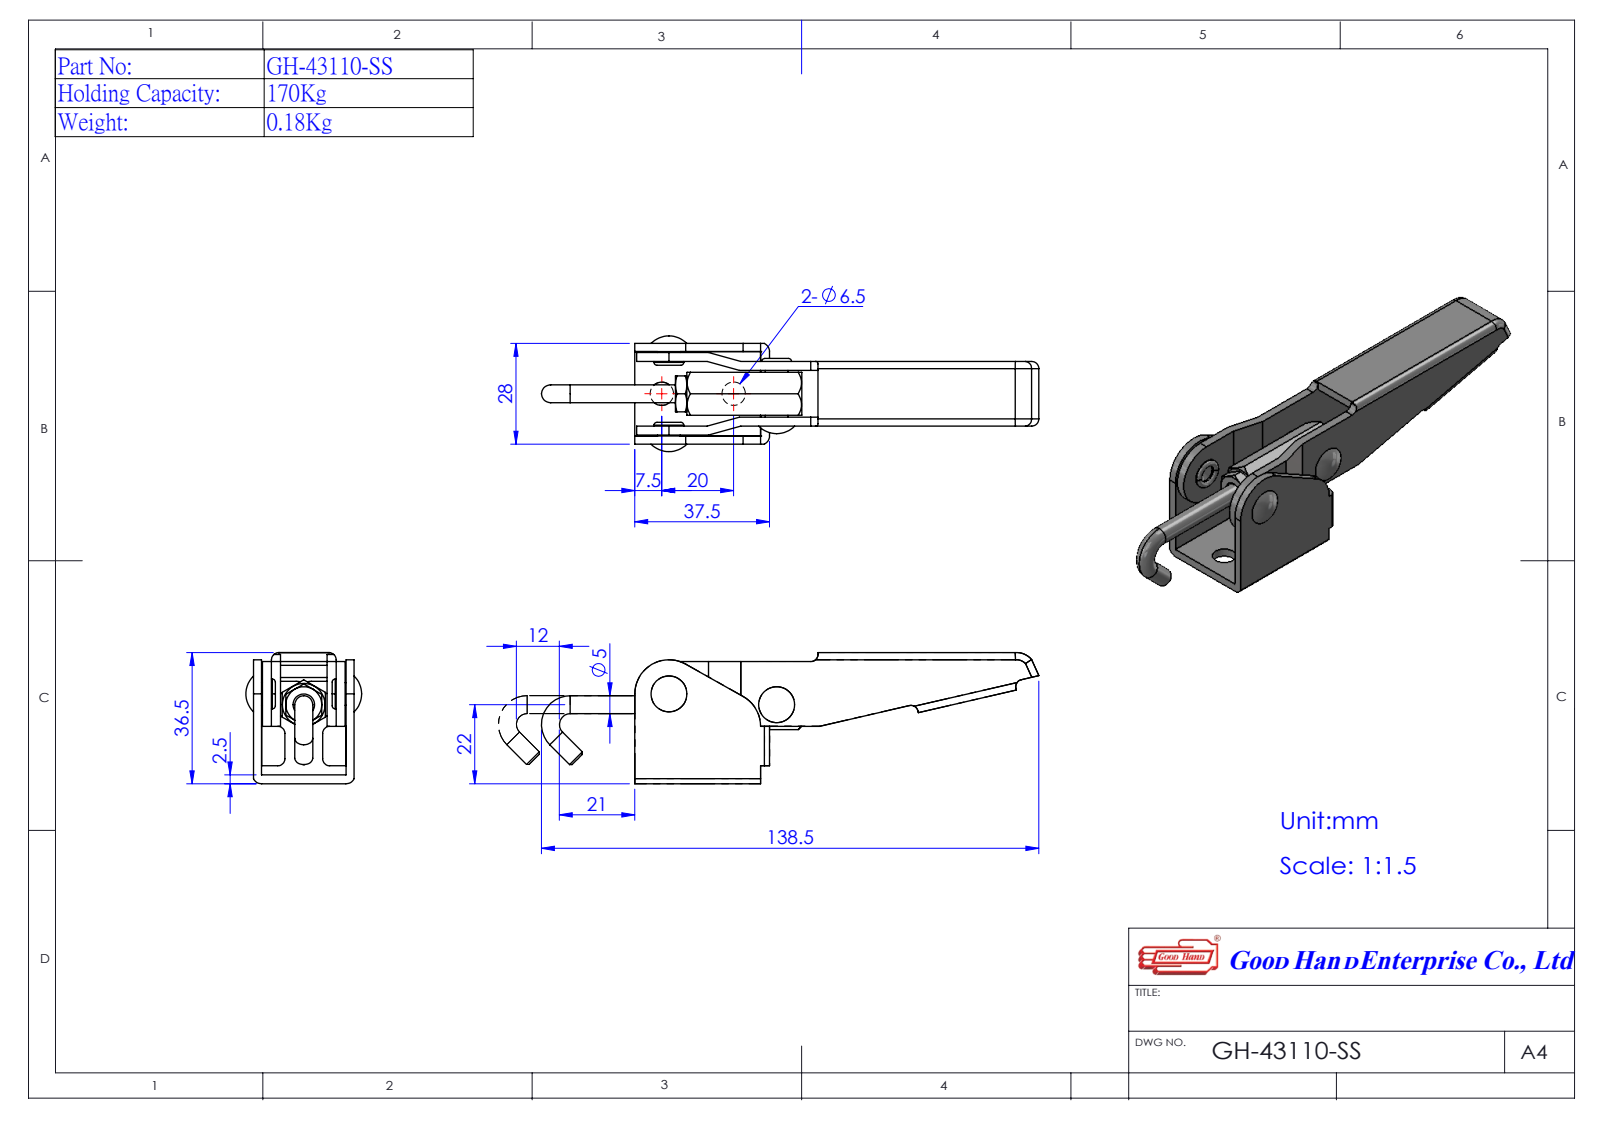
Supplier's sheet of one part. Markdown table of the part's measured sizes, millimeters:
| quantity | value |
| --- | --- |
| part name | GH-43110-SS(簡化); 4400144-1^GH-43110(簡化); Group3^GH-43110(簡化); Group2^GH-43110(簡化) (+1 more) |
| STEP written by | SolidWorks 2016 (AUTOMOTIVE_DESIGN) |
| units | millimeters |
| bodies | 4 solids, 197 faces (79 planar, 74 cylindrical, 44 other) |
| overall size | 138.49 × 36.51 × 32.2 |
| volume | 24 524 mm³ |
| surface area | 20 502 mm² |
| round holes (diameter × count) | 5 × 3, 6.6 × 2, 6 × 1, 7 × 1 |
| round bosses / shafts (diameter × count) | 8.3 × 1, 6.3 × 1, 5 × 1 |
| partial cylindrical surfaces (radius × count) | 2 × 17, 2.51 × 4, 9.5 × 2, 3.51 × 1, 5.51 × 1, 9 × 1 |
| main face-to-face distances | 2.5, 20.5, 5, 18, 23, 15.5, 2.75, 5.25, 2.25, 18.25 |
| hole center spacings | 20, 30.15 |
